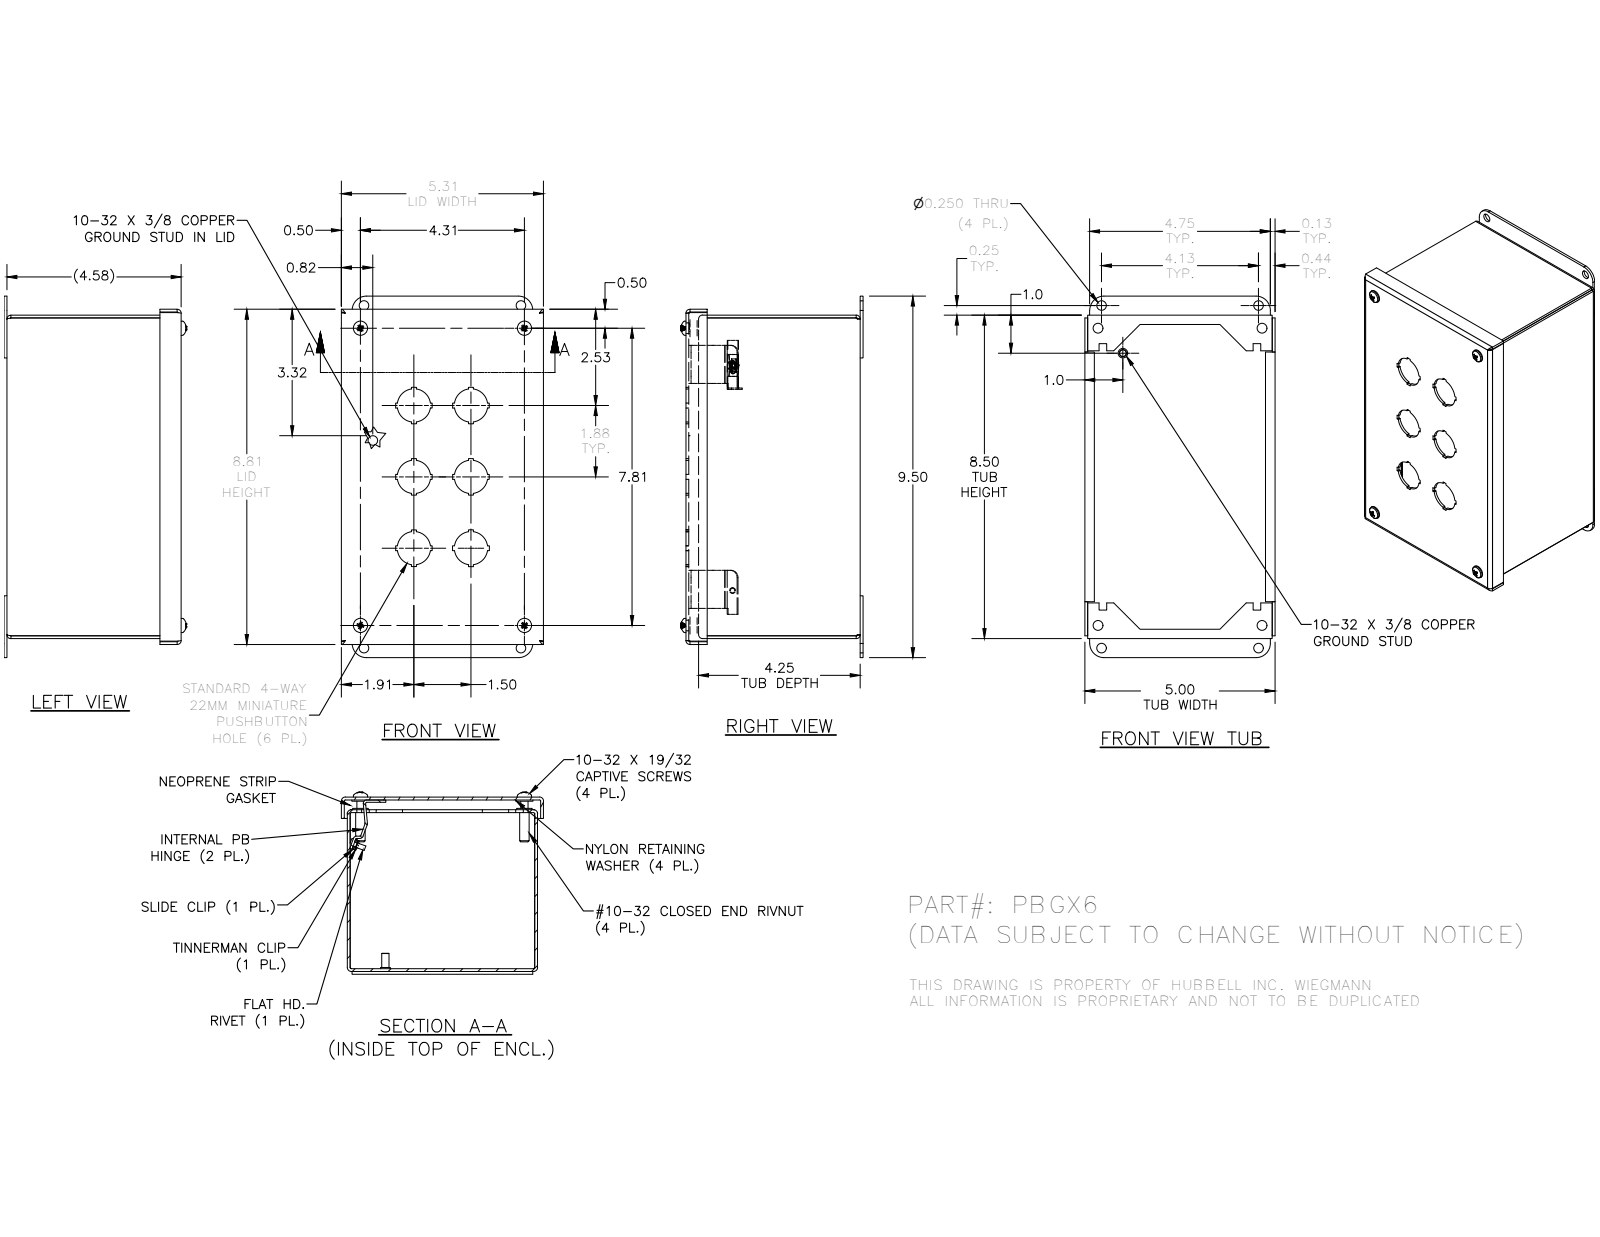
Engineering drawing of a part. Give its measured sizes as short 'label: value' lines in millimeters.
name: PBGX6BKP; 34984; 3285; 3185 (+8 more)
written by: Autodesk Inventor 2016 (AUTOMOTIVE_DESIGN)
unit: mm
bodies: 23 solids, 677 faces (411 planar, 152 cylindrical, 114 other)
size: 241.3 × 134.87 × 121.56
volume: 285 396 mm³; area: 314 670 mm²
holes: 6× ⌀22.22, 4× ⌀3.96, 4× ⌀4.98, 4× ⌀6.35, 4× ⌀6.53, 4× ⌀7.06, 4× ⌀7.14, 2× ⌀3.56
bosses: 6× ⌀4.83, 4× ⌀11.51, 4× ⌀10.31, 4× ⌀9.47, 4× ⌀6.3, 3× ⌀6.35, 1× ⌀3.17
rounds: 12× R0.79, 12× R2.67, 6× R4.78, 4× R2.27, 4× R2.29, 4× R9.53, 3× R0.8, 3× R1.59
face distances: 1.88, 114.5, 125.12, 116.38, 112.62, 214.02, 123.24, 127, 3.94, 215.9
hole spacings: 15.29, 60.99, 90.02, 105.42, 123.63, 134.79, 213.5, 38.1
